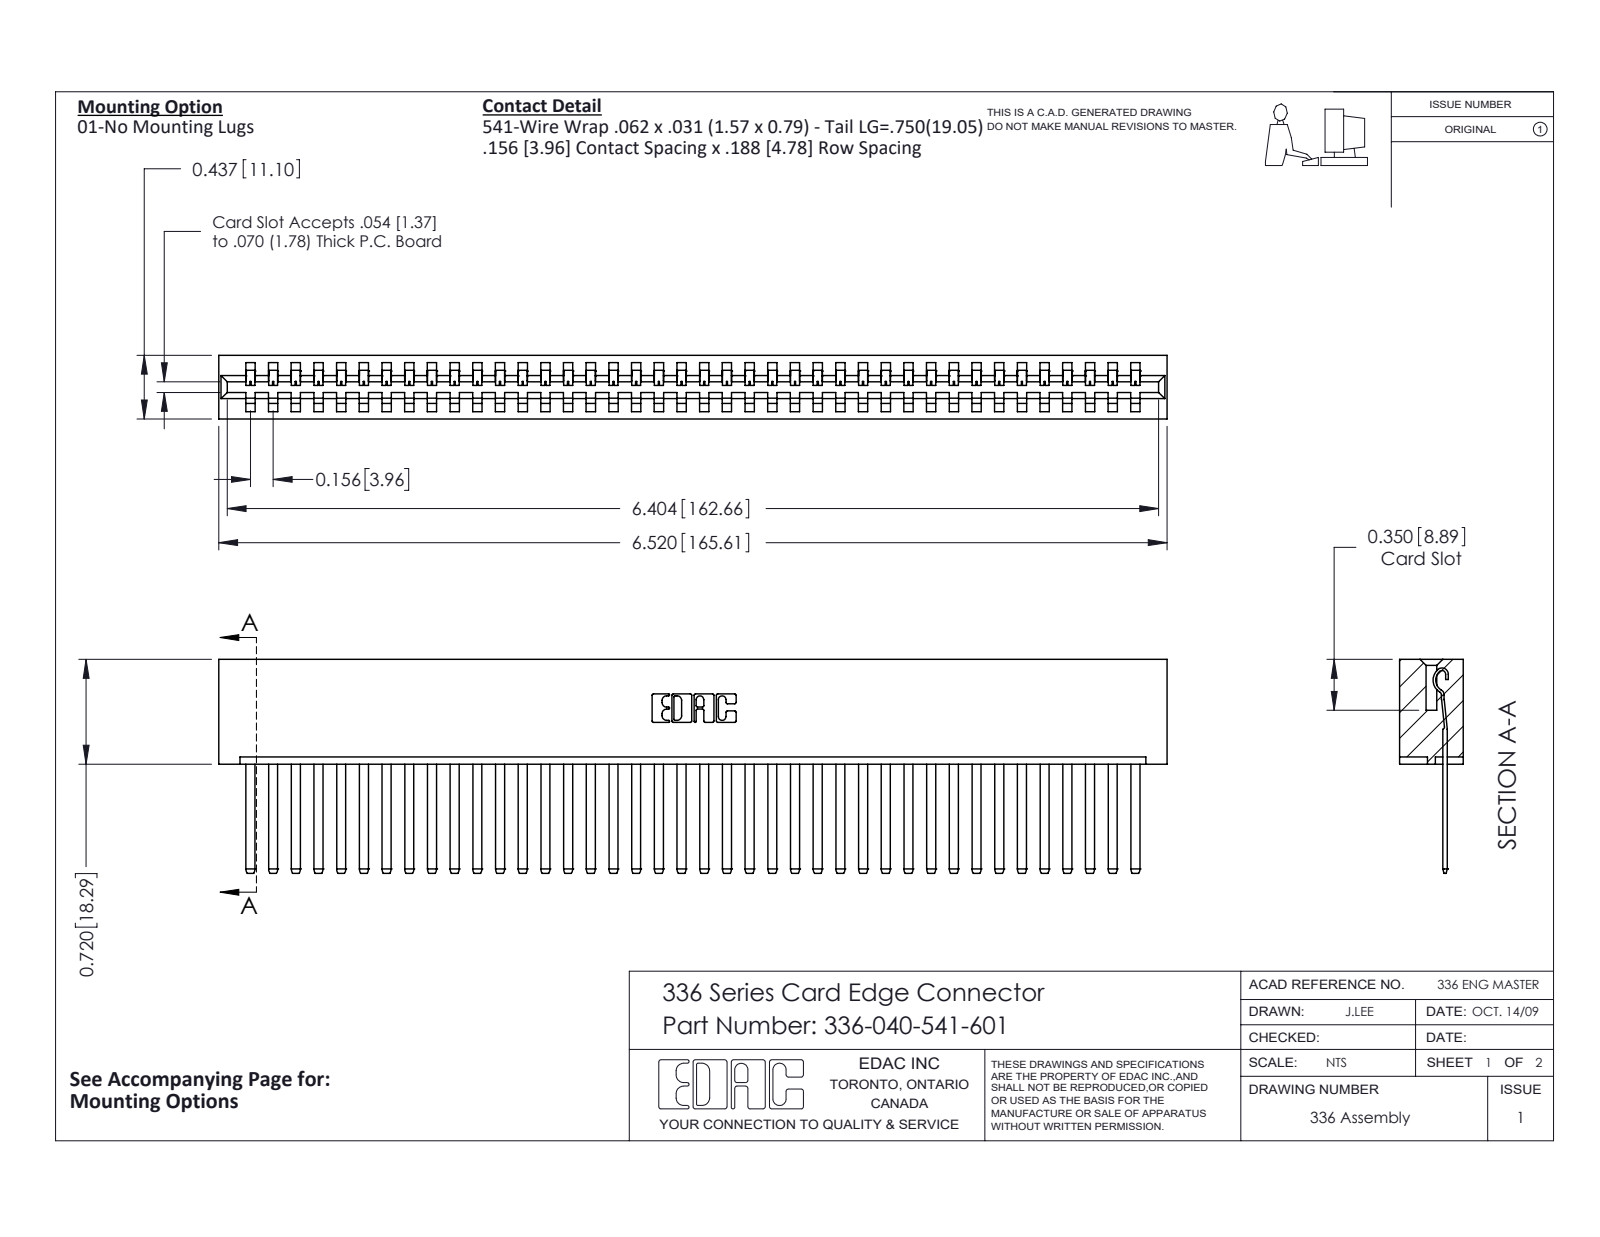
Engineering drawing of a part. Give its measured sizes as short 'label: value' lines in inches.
name: 336 Part_Lugless; 336-040-541-601; 336-290-001_336-290-541
written by: SolidWorks 2020 (CONFIG_CONTROL_DESIGN)
unit: in
bodies: 41 solids, 2106 faces (1426 planar, 680 cylindrical, 0 other)
size: 6.52 × 1.47 × 0.437
volume: 1.563 in³; area: 43.22 in²
rounds: 80× R0.004, 80× R0.056, 22× R0.01, 6× R0.007, 6× R0.031, 3× R0.026, 2× R0.022, 2× R0.04
face distances: 0.437, 0.181, 0.328, 0.14, 0.297, 0.109, 0.031, 0.256, 0.05, 0.387
